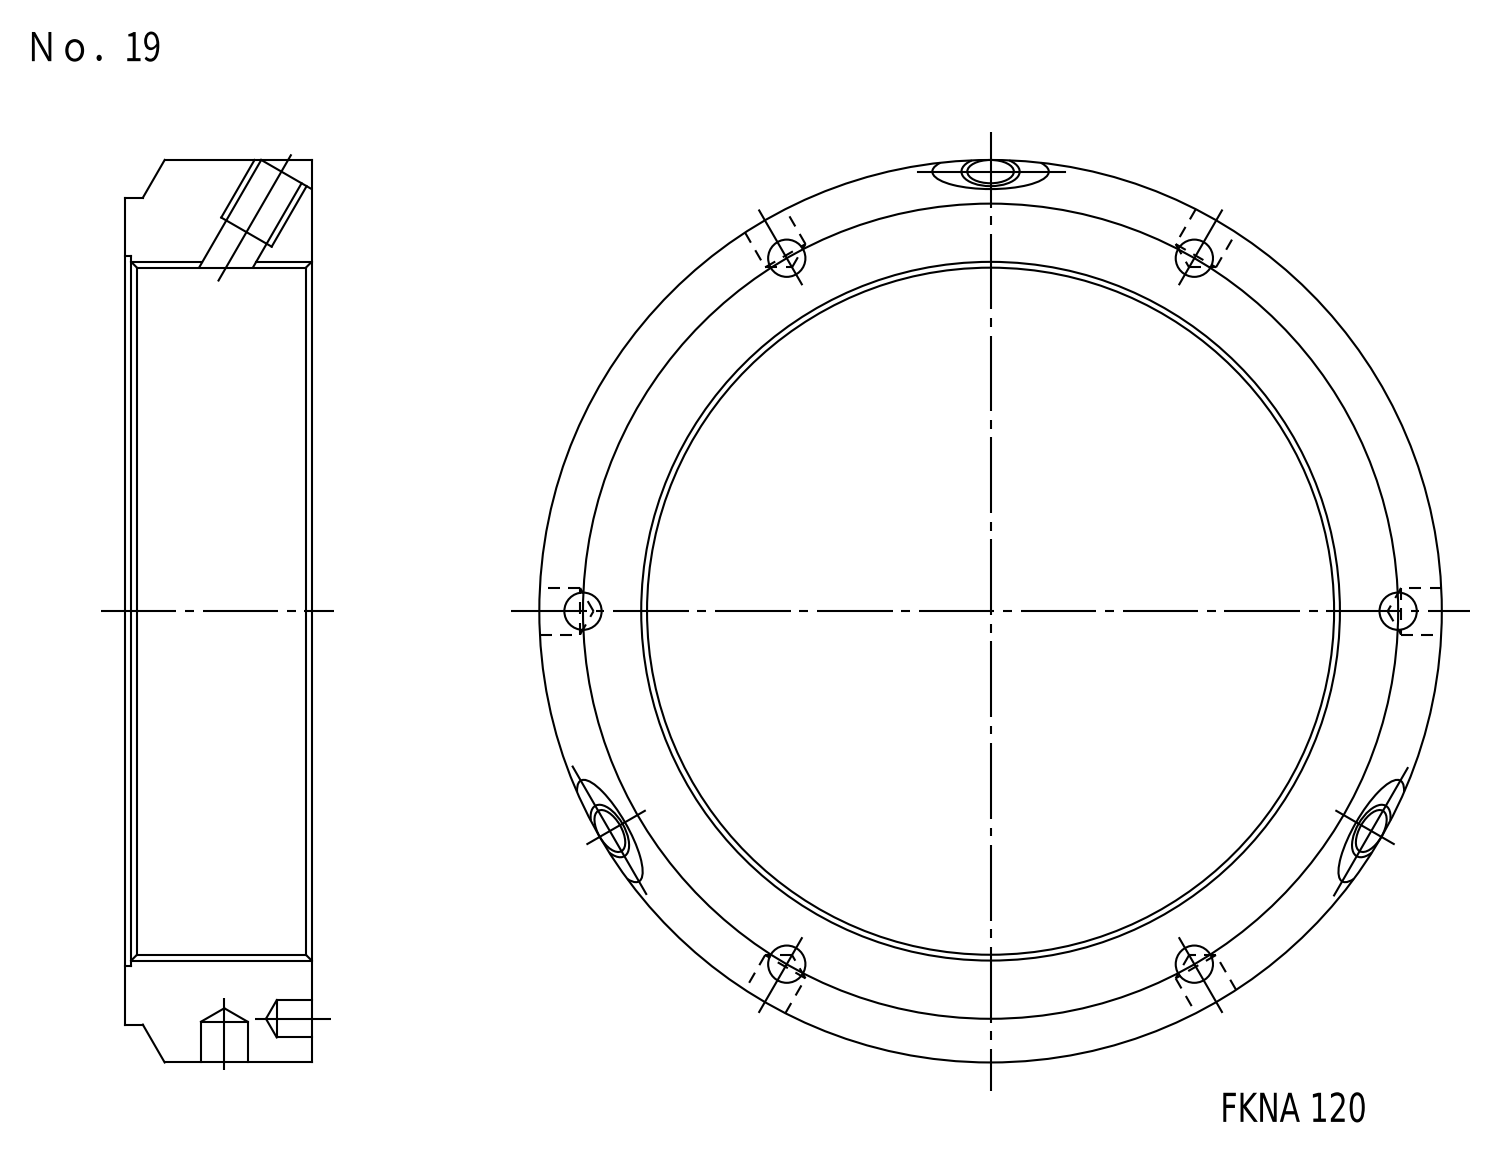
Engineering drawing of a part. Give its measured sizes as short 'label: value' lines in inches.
name: FKD FKNA120
written by: Autodesk Inventor LT (CONFIG_CONTROL_DESIGN)
unit: in
bodies: 1 solid, 44 faces (6 planar, 25 cylindrical, 13 other)
size: 6.102 × 6.102 × 1.26
volume: 13.74 in³; area: 67.95 in²
holes: 6× ⌀0.252, 3× ⌀0.315, 3× ⌀0.33, 3× ⌀0.402, 1× ⌀4.724, 1× ⌀4.803
bosses: 1× ⌀6.102, 1× ⌀5.591
rounds: 3× R0.787
face distances: 1.26, 0.059, 1.201
hole spacings: 2.756, 4.773, 5.512
